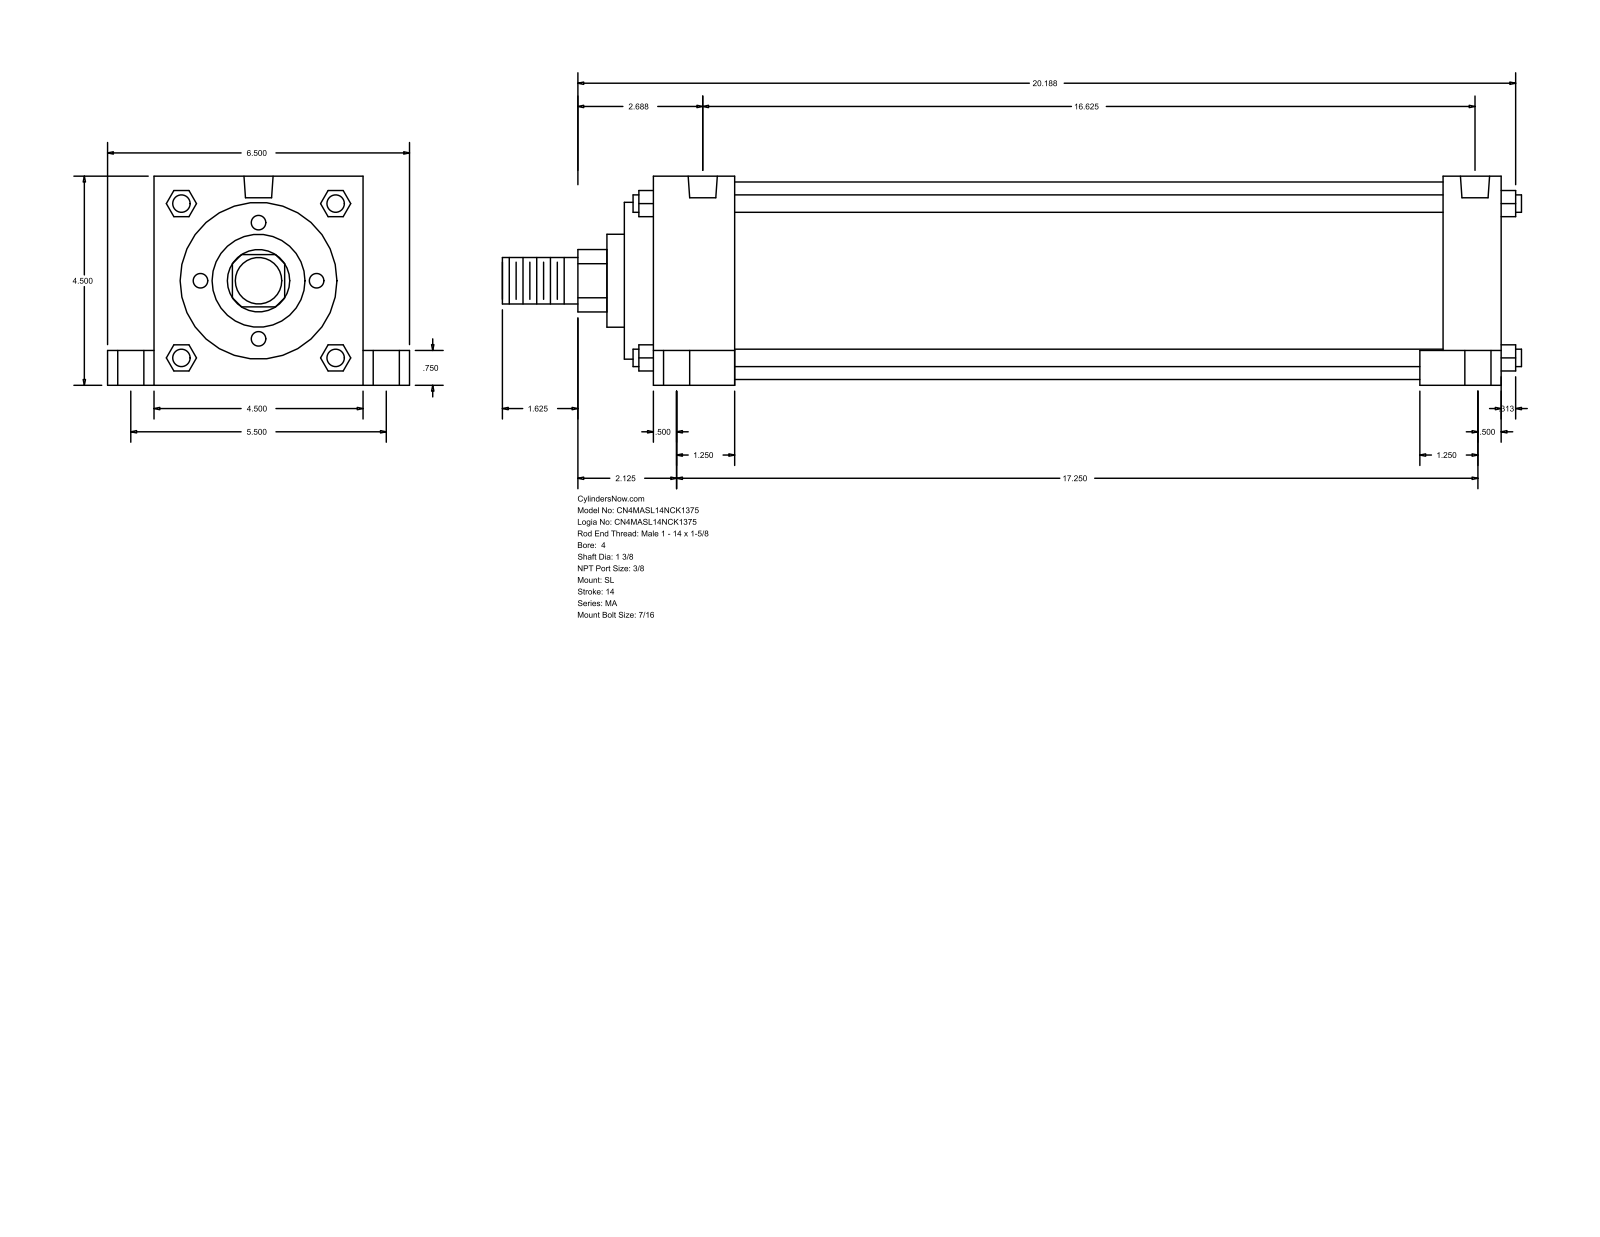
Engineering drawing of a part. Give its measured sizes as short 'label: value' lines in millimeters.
name: MA_SL__0400_1.375
written by: GSSL Pune (CONFIG_CONTROL_DESIGN)
unit: mm
bodies: 0 solids, 150 faces (113 planar, 37 cylindrical, 0 other)
size: 557.21 × 165.1 × 114.3
holes: 4× ⌀11.11, 4× ⌀14.29, 4× ⌀20.64, 2× ⌀15.93
bosses: 4× ⌀9.53, 1× ⌀107.95, 1× ⌀85.72, 1× ⌀50.8, 1× ⌀34.92, 1× ⌀25.4
rounds: 1× R17.06
face distances: 114.3, 463.55, 387.35, 479.42, 15.87, 60.32, 44.45, 419.1, 447.67, 431.8
hole spacings: 4.77, 69.87, 70.14, 71.29, 72.4, 139.7, 412.74, 417.51
